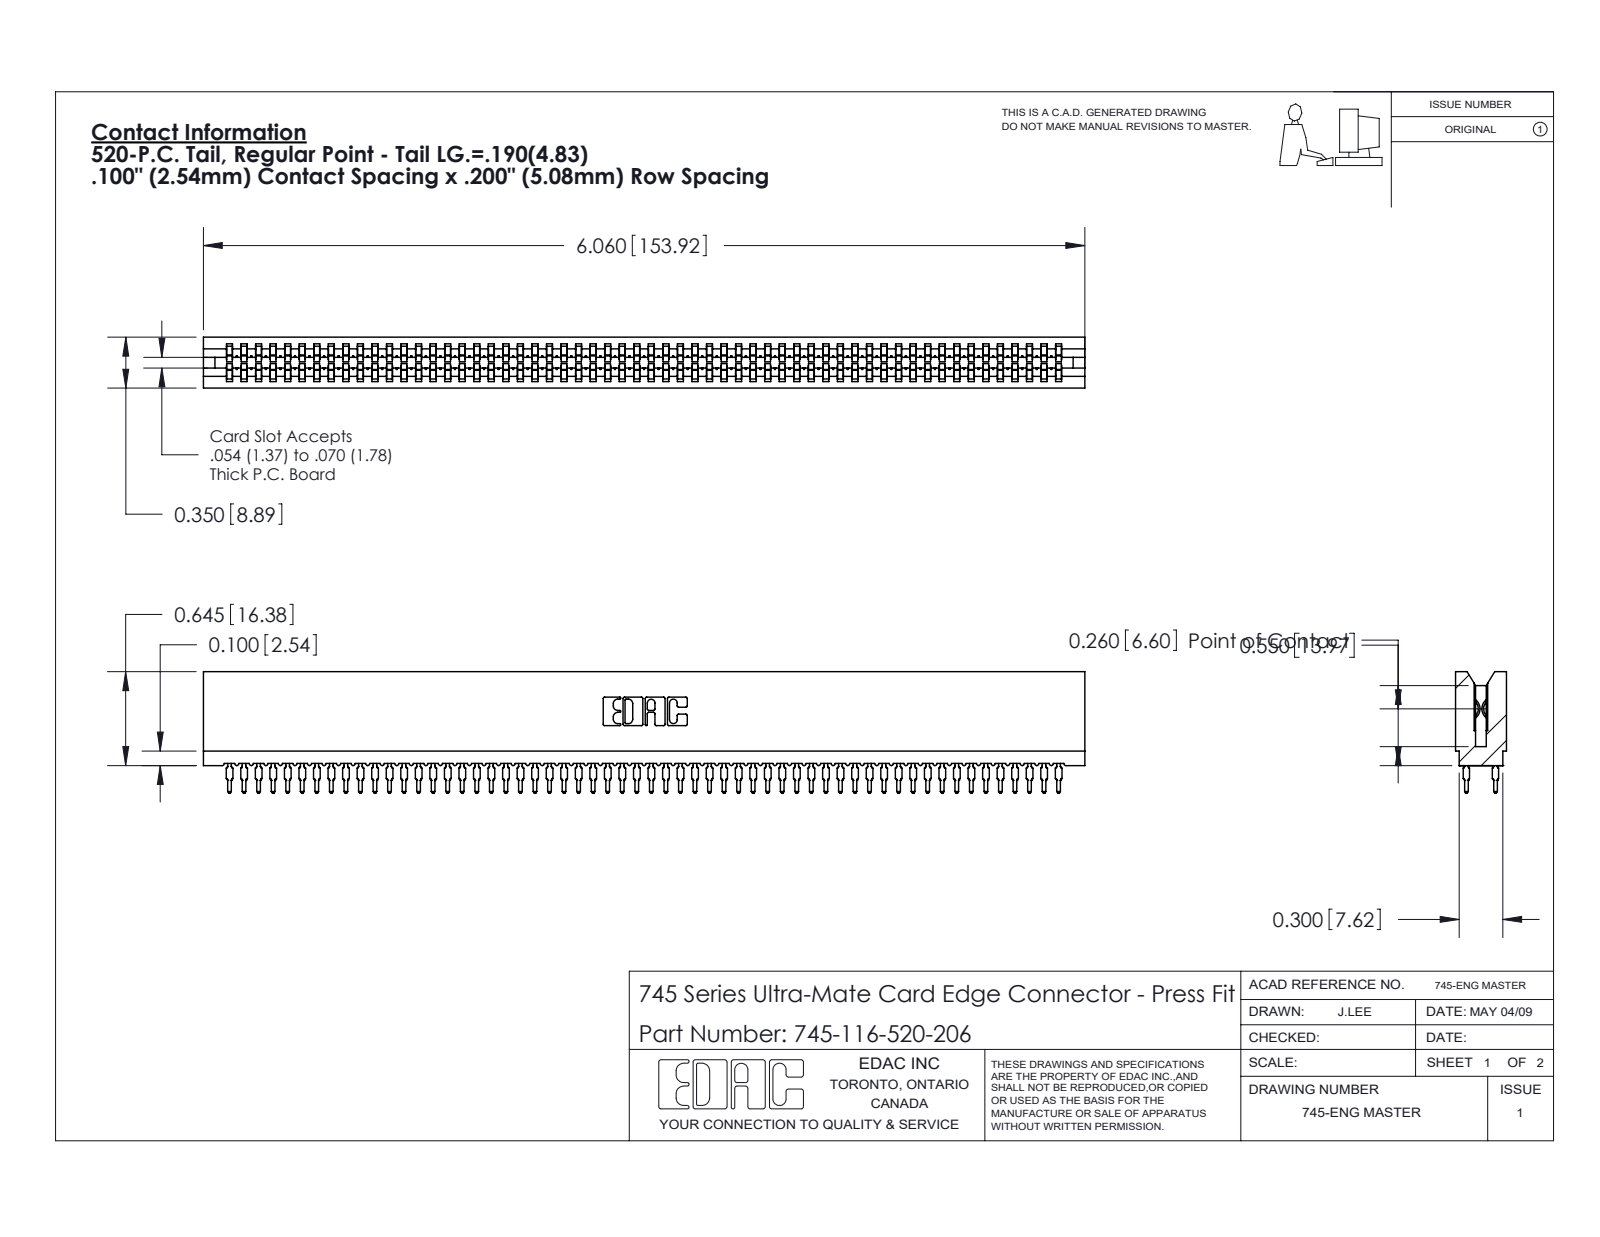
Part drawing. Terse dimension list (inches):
name: 745 Part_Insulator Option - 06; 745-292-001_520; 745-116-520-206
written by: SolidWorks 2020 (CONFIG_CONTROL_DESIGN)
unit: in
bodies: 117 solids, 10478 faces (5392 planar, 2070 cylindrical, 3016 other)
size: 6.06 × 0.836 × 0.35
volume: 0.833 in³; area: 42.78 in²
rounds: 232× R0.021, 116× R0.015, 22× R0.01, 8× R0.005, 8× R0.011, 6× R0.007, 6× R0.031, 3× R0.026
face distances: 0.35, 0.063, 0.287, 0.045, 0.305, 0.018, 0.243, 0.138, 0.212, 0.093
